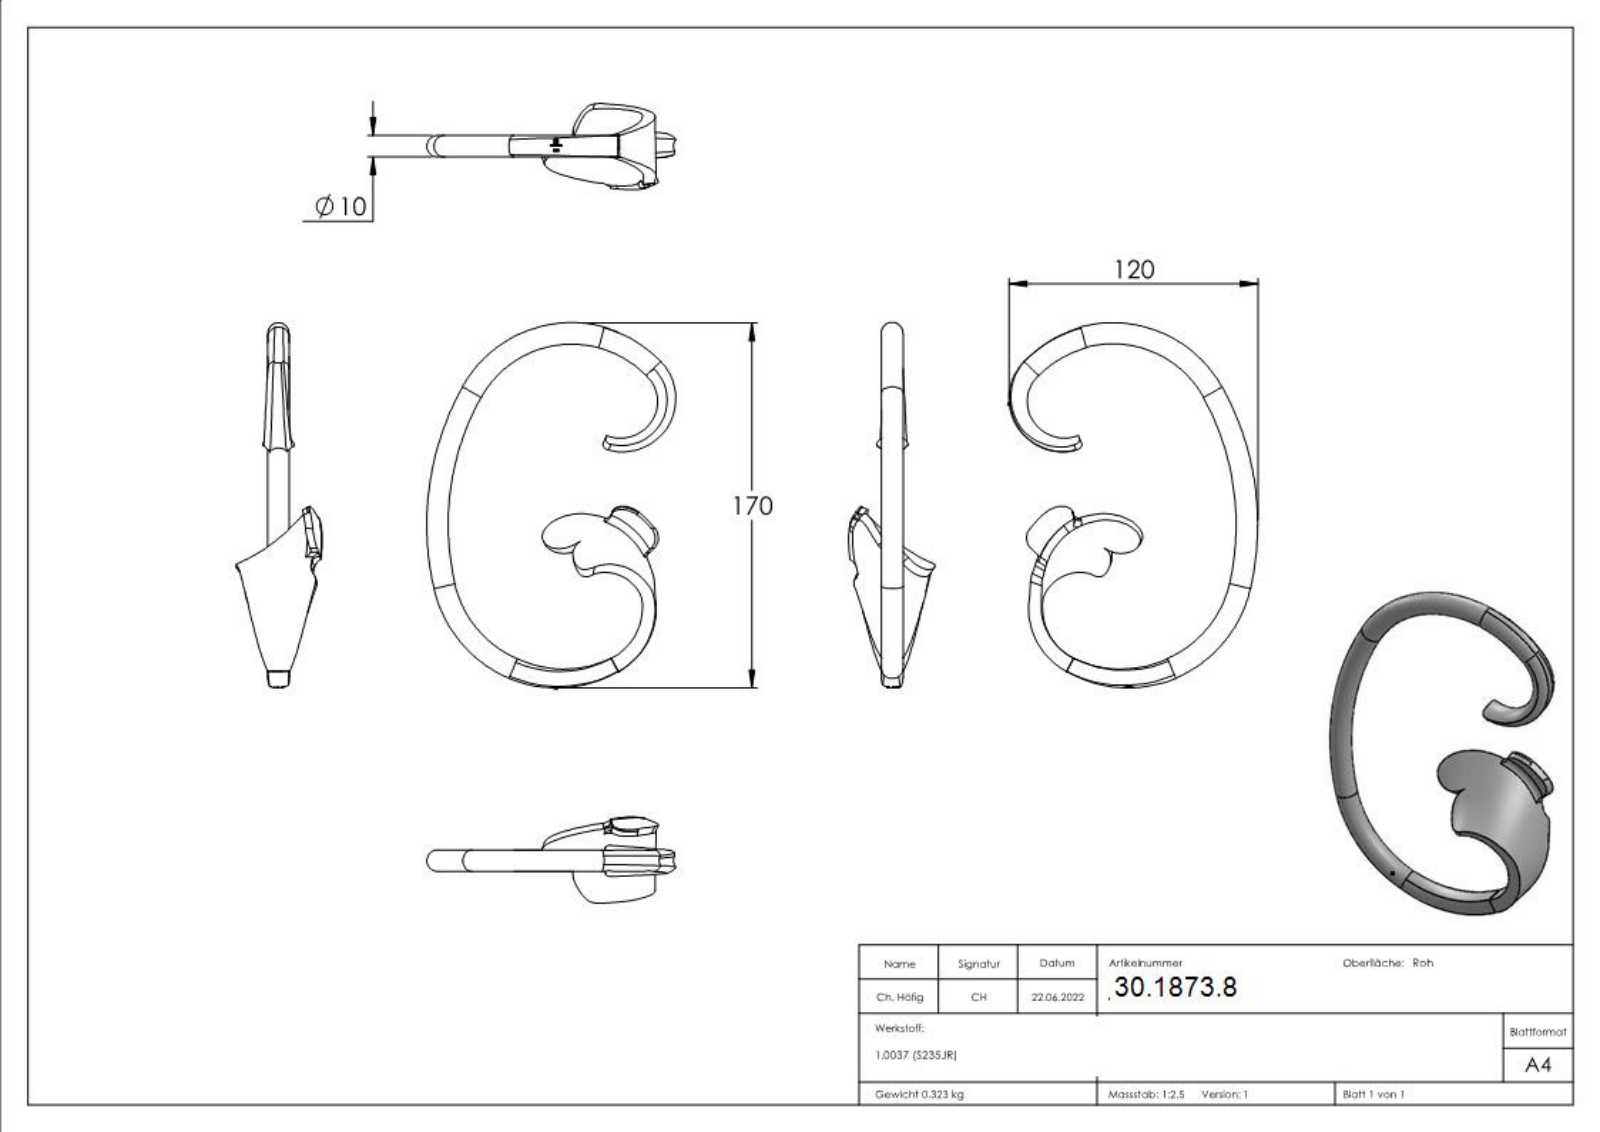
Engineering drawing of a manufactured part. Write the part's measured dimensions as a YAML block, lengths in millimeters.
part_name: "5562"
step_written_by: "SolidWorks 2018 (CONFIG_CONTROL_DESIGN)"
units: millimeters
bodies: {solids: 1, faces: 277, planar: 101, cylindrical: 0, other: 176}
overall_size: [169.36, 115.59, 39.93]
volume: 41438
surface_area: 18450
face_to_face_distances: [1.76, 2.32, 1.96, 0.49, 1.78, 0.47, 2.31, 1.21, 0.83, 1.49]
